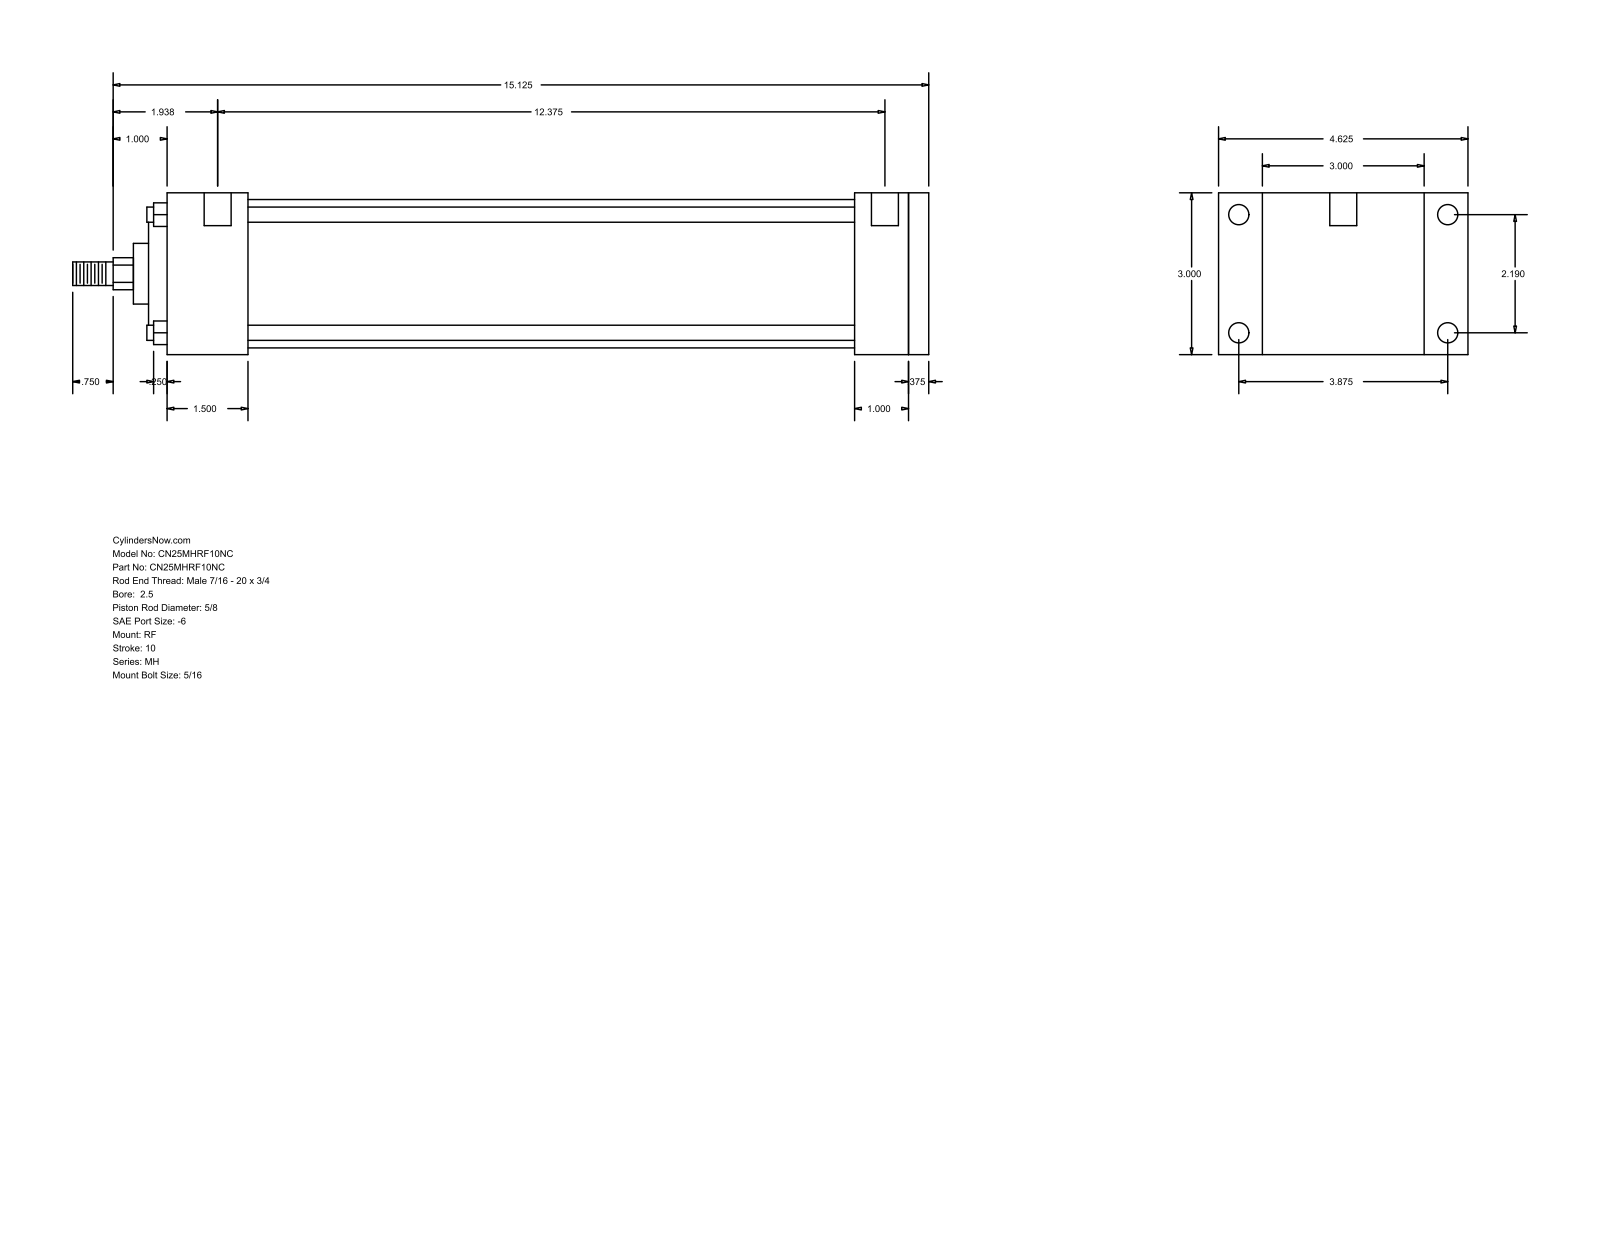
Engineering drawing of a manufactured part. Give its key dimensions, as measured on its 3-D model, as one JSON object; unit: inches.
{"part_name": "MH_RF__0250_0.625", "step_written_by": "GSSL Pune (CONFIG_CONTROL_DESIGN)", "units": "inches", "bodies": {"solids": 0, "faces": 94, "planar": 65, "cylindrical": 29, "other": 0}, "overall_size": [15.875, 4.625, 3], "round_holes": [[0.219, 4], [0.375, 4], [0.5, 2]], "round_bosses_or_shafts": [[0.281, 4], [2.75, 1], [2.187, 1], [1.125, 1], [0.625, 1], [0.437, 1]], "partial_cylinders_radius": [[0.297, 1]], "face_to_face_distances": [3, 0.375, 14.125, 13.75, 1, 1.375, 1.5, 12.75, 11.25, 12.25], "hole_center_spacings": [2.19, 3.875, 4.451, 12.687, 0.125, 0.187, 12.375, 12.5]}
